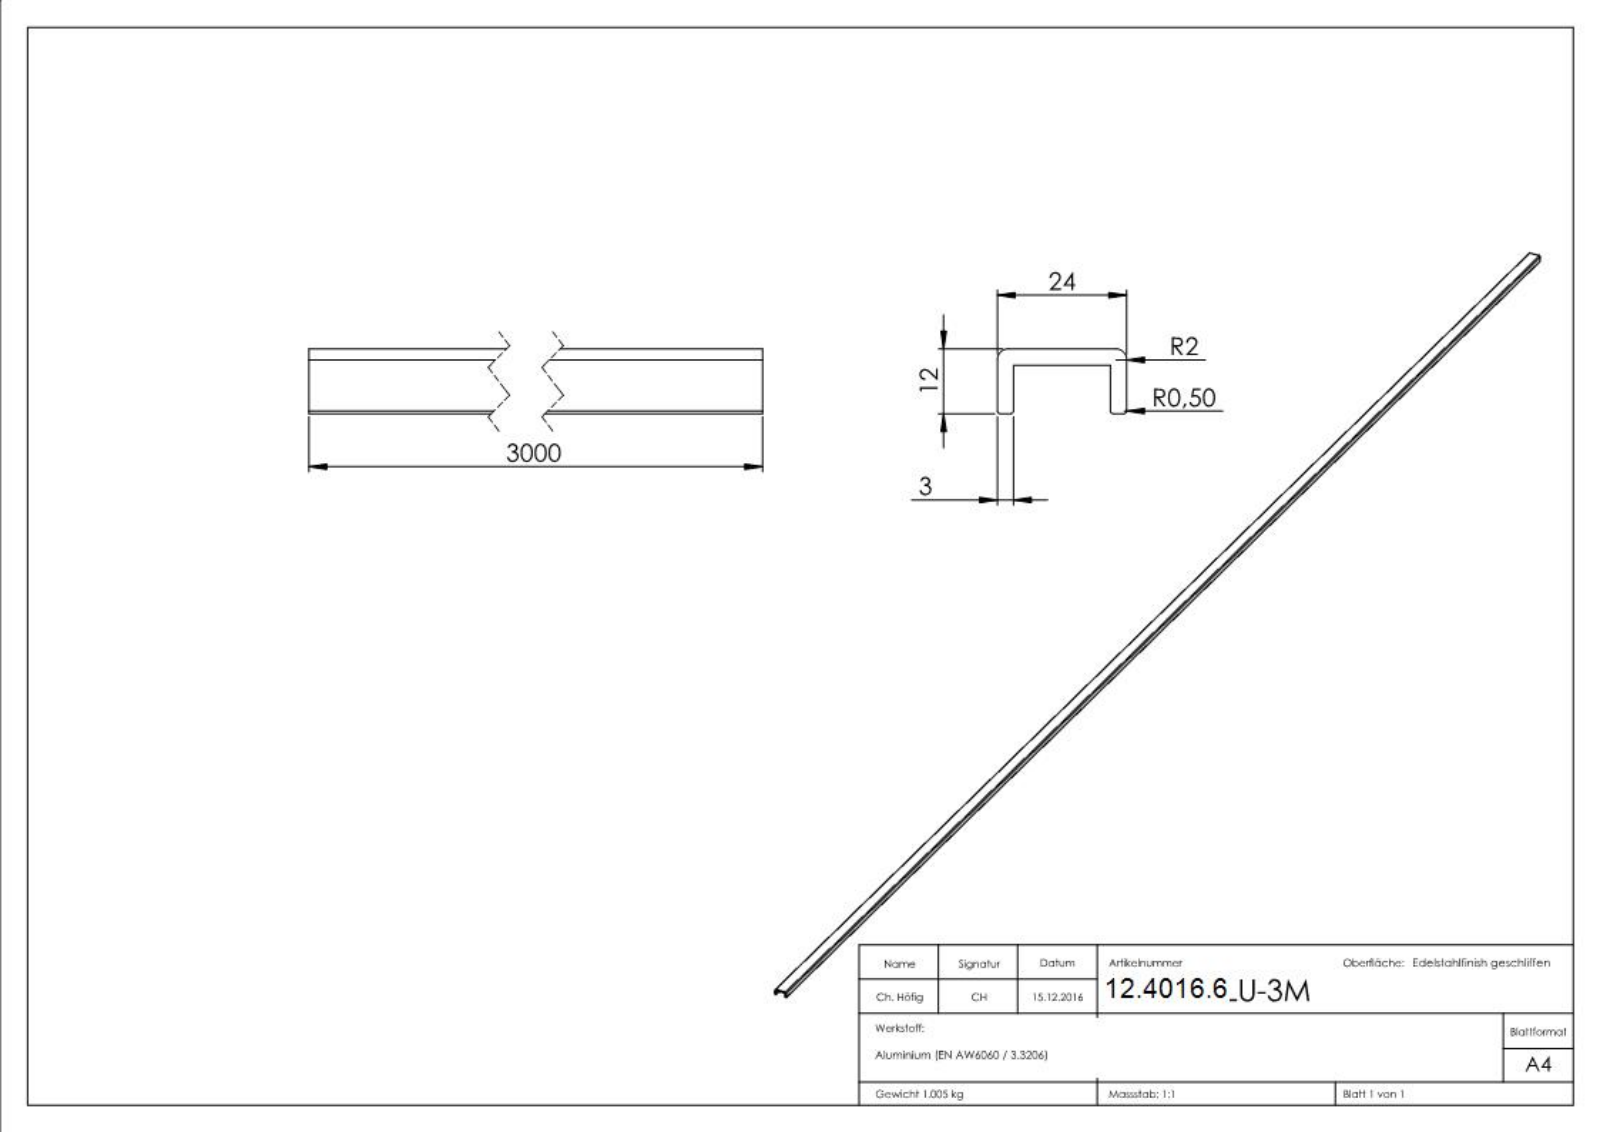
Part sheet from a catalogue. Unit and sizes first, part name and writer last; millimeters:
Units: millimetres
Overall size (bounding box): 3000 × 24 × 12
Partial cylindrical surfaces — rounded edges, fillets, slot ends (radius × count): R0.5 ×4, R2 ×2
Main face-to-face distances: 3, 21, 24, 18, 9, 12, 3000, 2.9, 18.1, 21.1
Volume: 372 205 mm³ · Surface area: 262 534 mm²
Bodies: 1 solid, 289 faces (149 planar, 6 cylindrical, 134 other)
Part name (STEP PRODUCT): 80538-ALU-3M
STEP written by: SolidWorks 2015 (CONFIG_CONTROL_DESIGN)
